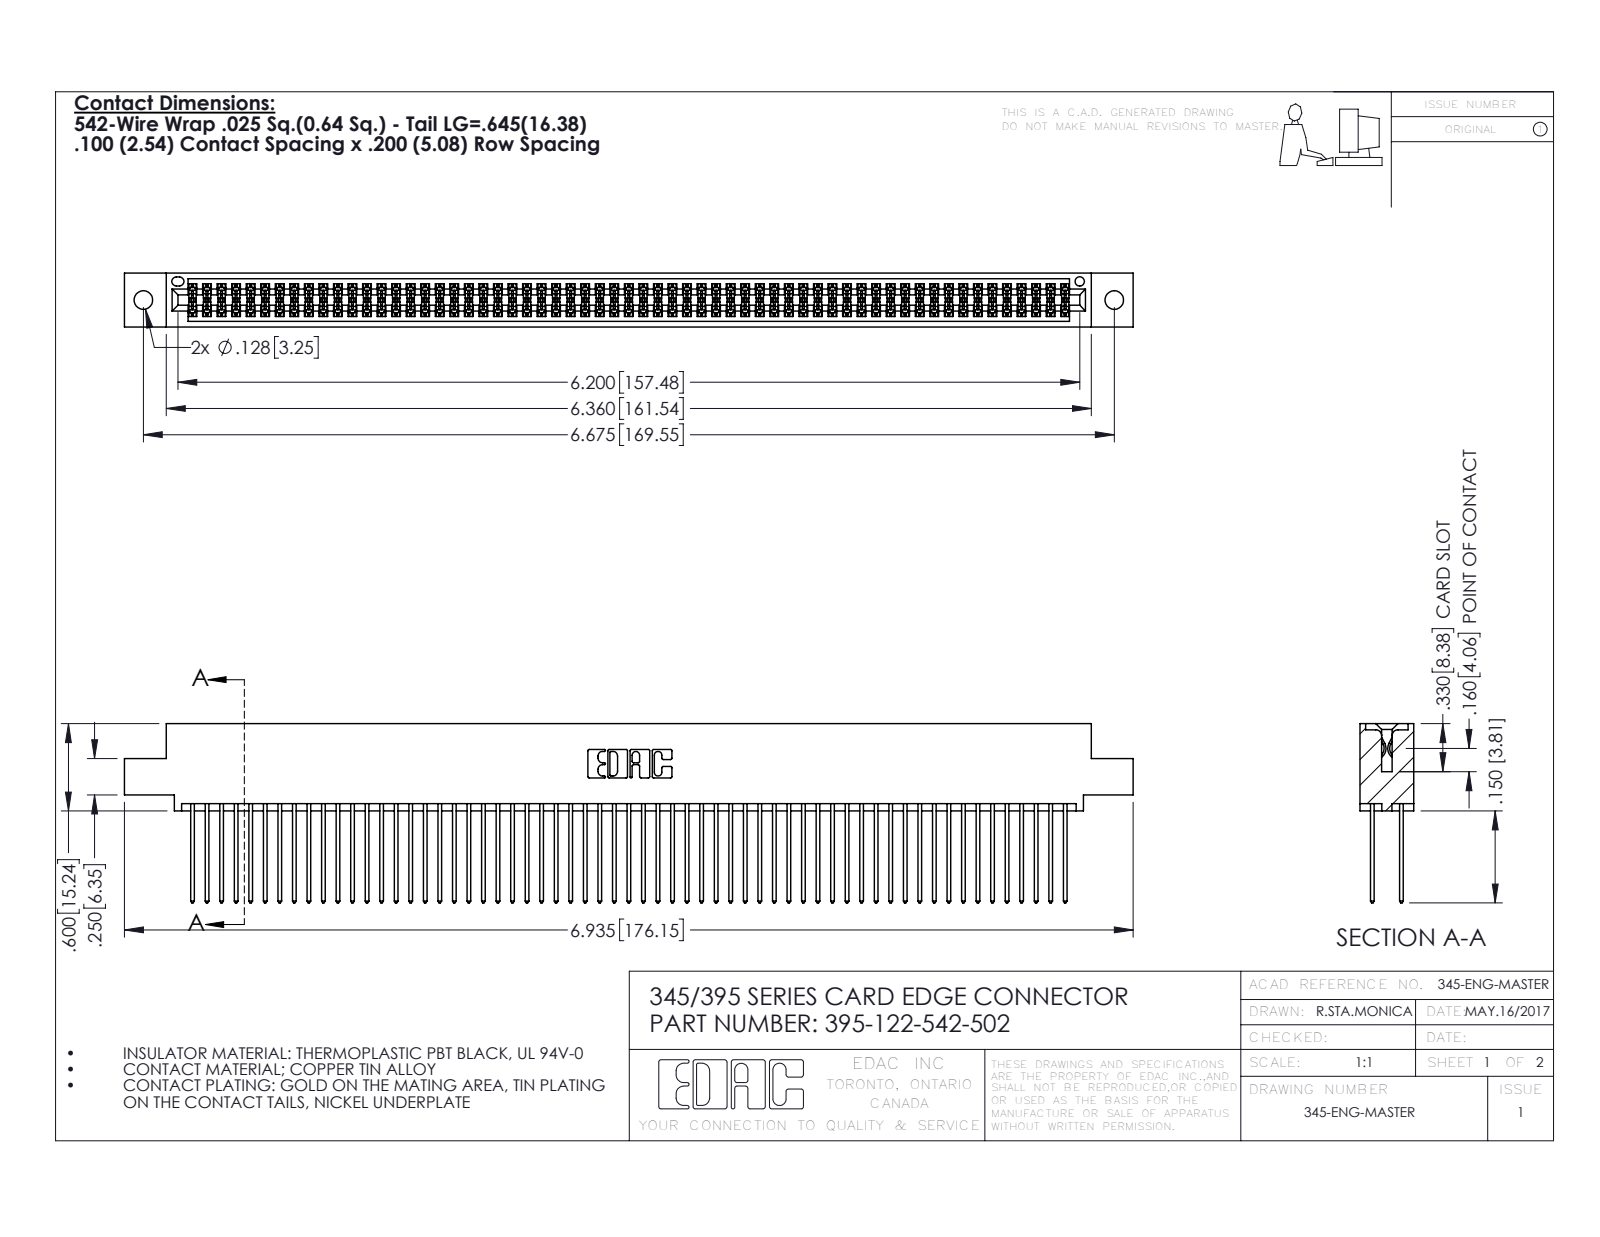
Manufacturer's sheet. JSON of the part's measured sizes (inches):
{"part_name": "395-122-542-502; 345-292-001_345-293-142; 345 Part_0.110 Offset - 0.128 Dia", "step_written_by": "SolidWorks 2016 (CONFIG_CONTROL_DESIGN)", "units": "inches", "bodies": {"solids": 123, "faces": 6230, "planar": 4110, "cylindrical": 2120, "other": 0}, "overall_size": [6.935, 1.232, 0.37], "volume_in3": 1.083, "surface_area_in2": 45.07, "round_holes": [[0.128, 2], [0.064, 1]], "partial_cylinders_radius": [[0.006, 183], [0.01, 122], [0.01, 22], [0.007, 6], [0.031, 6], [0.026, 3], [0.014, 2], [0.019, 2]], "face_to_face_distances": [0.072, 0.298, 0.2, 0.098, 0.272, 0.025, 0.225, 0.37, 0.175, 0.149], "hole_center_spacings": [0.27, 6.439, 6.675]}
